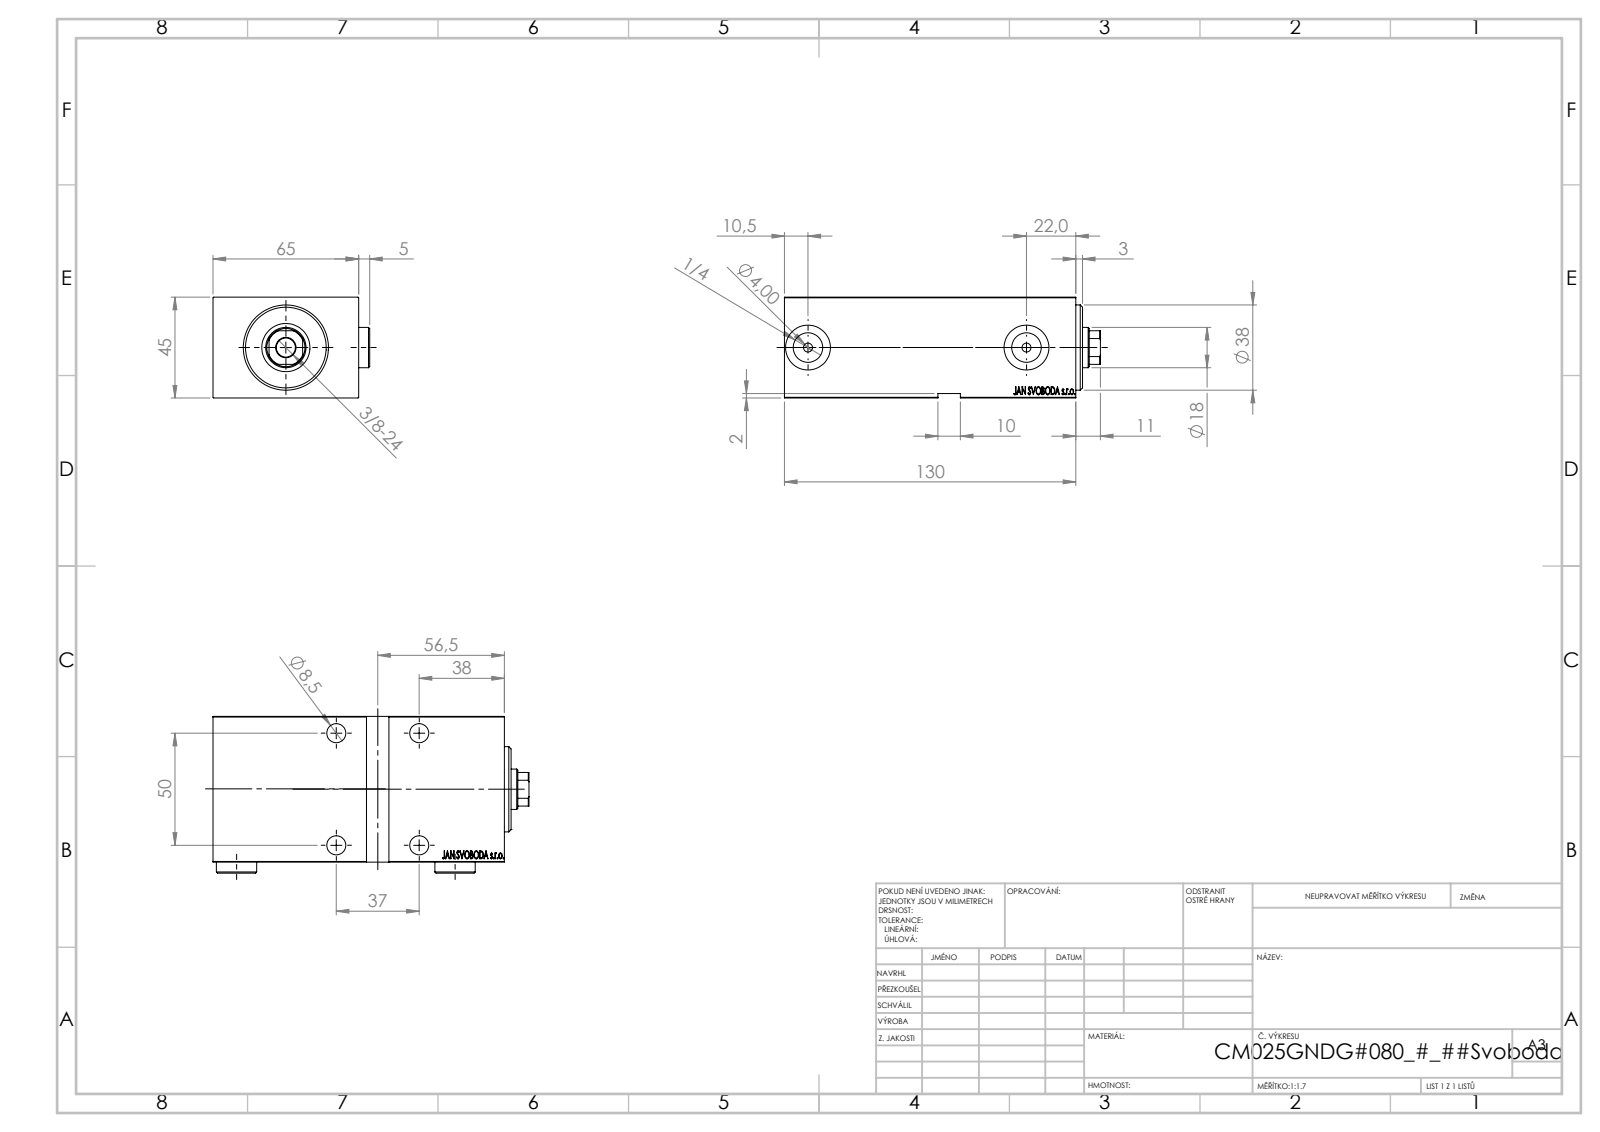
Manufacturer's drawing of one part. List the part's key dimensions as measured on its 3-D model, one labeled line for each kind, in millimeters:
Part name (STEP PRODUCT): V450CM_VC_G; Zatka_OIL_PORT; V450CM_G_Body; V450CM_G_VCP
STEP written by: SolidWorks 2019 (CONFIG_CONTROL_DESIGN)
Units: millimetres
Bodies: 5 solids, 913 faces (445 planar, 70 cylindrical, 398 other)
Overall size (bounding box): 141 × 69.9 × 45
Volume: 344 529 mm³ · Surface area: 67 400 mm²
Round holes (diameter × count): ⌀8.5 ×5, ⌀13.5 ×4, ⌀4 ×2, ⌀13.16 ×2, ⌀20 ×2, ⌀18 ×1, ⌀21.5 ×1, ⌀25 ×1, ⌀27 ×1, ⌀35 ×1
Round bosses / shafts (diameter × count): ⌀18 ×2, ⌀38 ×1
Partial cylindrical surfaces — rounded edges, fillets, slot ends (radius × count): R8.5 ×1
Main face-to-face distances: 45, 65, 130, 6, 64.9, 119, 5, 124, 8, 125
Hole centre spacings: 37, 50, 62.2, 97.5
